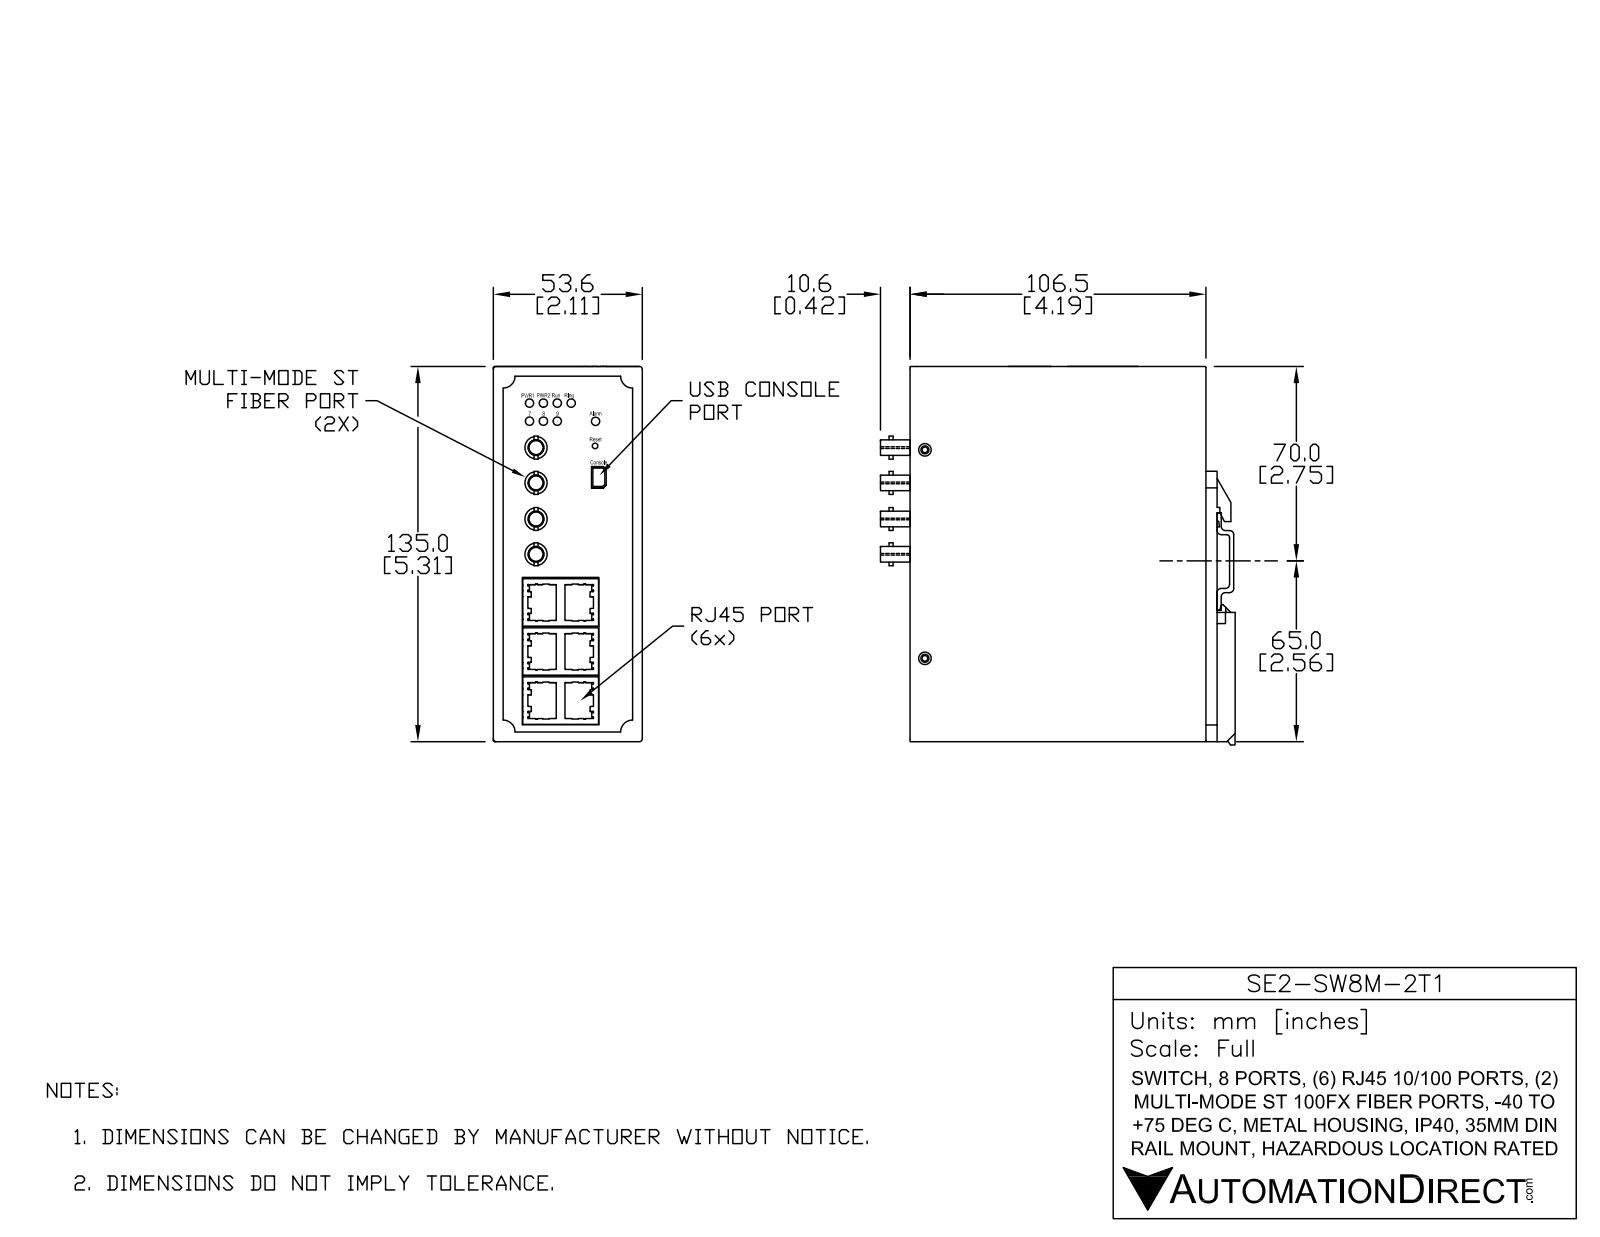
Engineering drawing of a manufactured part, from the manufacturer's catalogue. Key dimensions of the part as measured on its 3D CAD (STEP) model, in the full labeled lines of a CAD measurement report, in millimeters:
Part name (STEP PRODUCT): SE2-SW8M-2T1; Weidmiller_DINRC_1; SE2-SW8M-2T1_1
STEP written by: SolidWorks 2017 (AUTOMOTIVE_DESIGN)
Units: millimetres
Bodies: 0 solids, 1168 faces (819 planar, 55 cylindrical, 294 other)
Overall size (bounding box): 135 × 127.7 × 54
Round holes (diameter × count): ⌀5 ×4
Round bosses / shafts (diameter × count): ⌀4.5 ×5, ⌀8 ×4, ⌀7 ×4, ⌀5.6 ×4, ⌀5.1 ×4, ⌀5.5 ×2, ⌀1.4 ×1
Partial cylindrical surfaces — rounded edges, fillets, slot ends (radius × count): R1 ×4, R2.4 ×4, R5 ×4, R4.3 ×3, R2 ×2, R4 ×2, R4.3 ×1
Main face-to-face distances: 53.6, 135, 106.1, 4.5, 110.6, 0.4, 111, 11, 106.5, 4.7
Hole centre spacings: 12.7, 25.7, 13, 38.4
